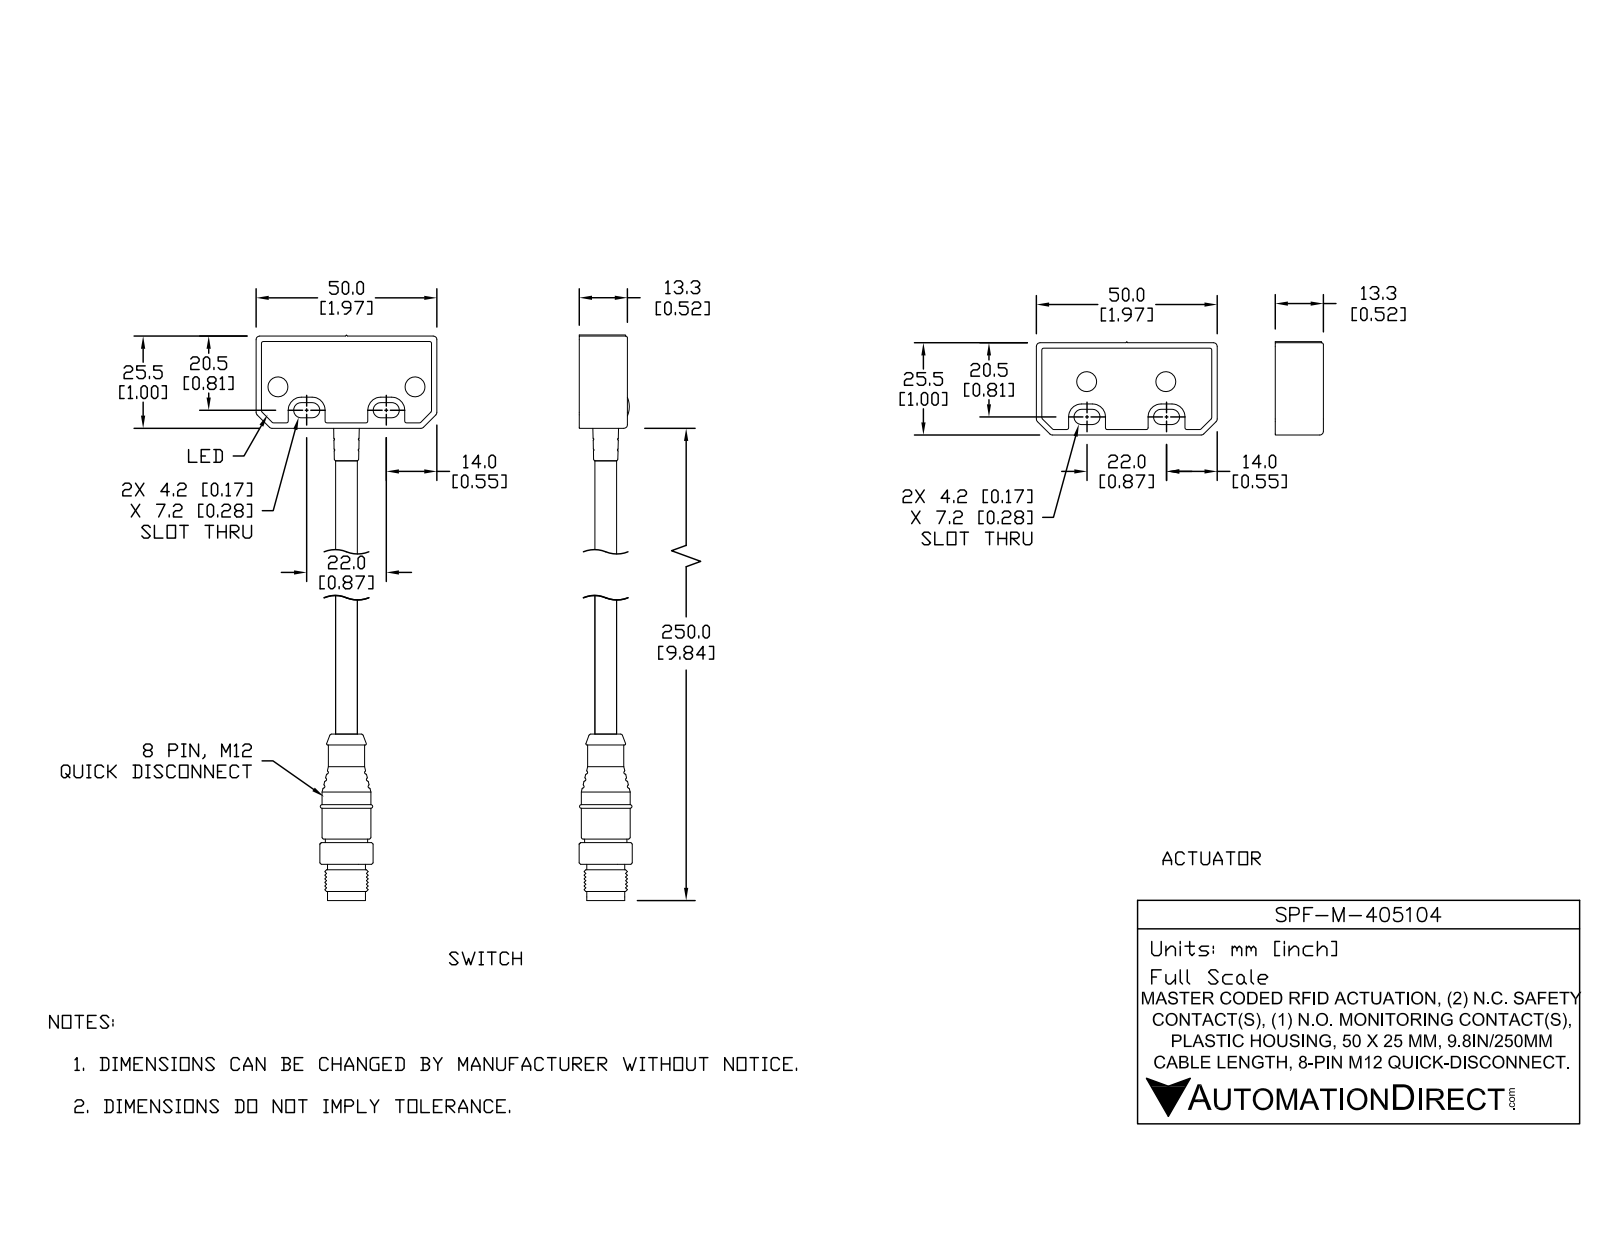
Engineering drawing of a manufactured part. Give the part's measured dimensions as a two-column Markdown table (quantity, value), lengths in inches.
| quantity | value |
| --- | --- |
| part name | SPF-M-405104_1; SPF-M-405104; SPF-M-405104_2 |
| STEP written by | SolidWorks 2017 (AUTOMOTIVE_DESIGN) |
| units | inches |
| bodies | 13 solids, 1506 faces (632 planar, 472 cylindrical, 402 other) |
| overall size | 11.89 × 1.969 × 0.579 |
| volume | 1.486 in³ |
| surface area | 43.7 in² |
| round holes (diameter × count) | 0.197 × 4, 0.119 × 1, 0.173 × 1, 0.213 × 1, 0.232 × 1, 0.276 × 1, 0.327 × 1, 0.465 × 1 |
| round bosses / shafts (diameter × count) | 0.031 × 10, 0.079 × 4, 0.193 × 2, 0.531 × 1, 0.461 × 1, 0.413 × 1, 0.394 × 1, 0.374 × 1 |
| partial cylindrical surfaces (radius × count) | 0.02 × 132, 0.039 × 36, 0.079 × 8, 0.083 × 8, 0.142 × 8, 0.181 × 8, 0.012 × 6, 0.14 × 4 |
| main face-to-face distances | 0.059, 0.457, 0.398, 0.047, 0.445, 0.504, 1.043, 0.098, 0.945, 1.909 |
| hole center spacings | 0.221, 0.862, 1.062, 1.065, 1.283, 1.492, 1.55, 1.559 |
